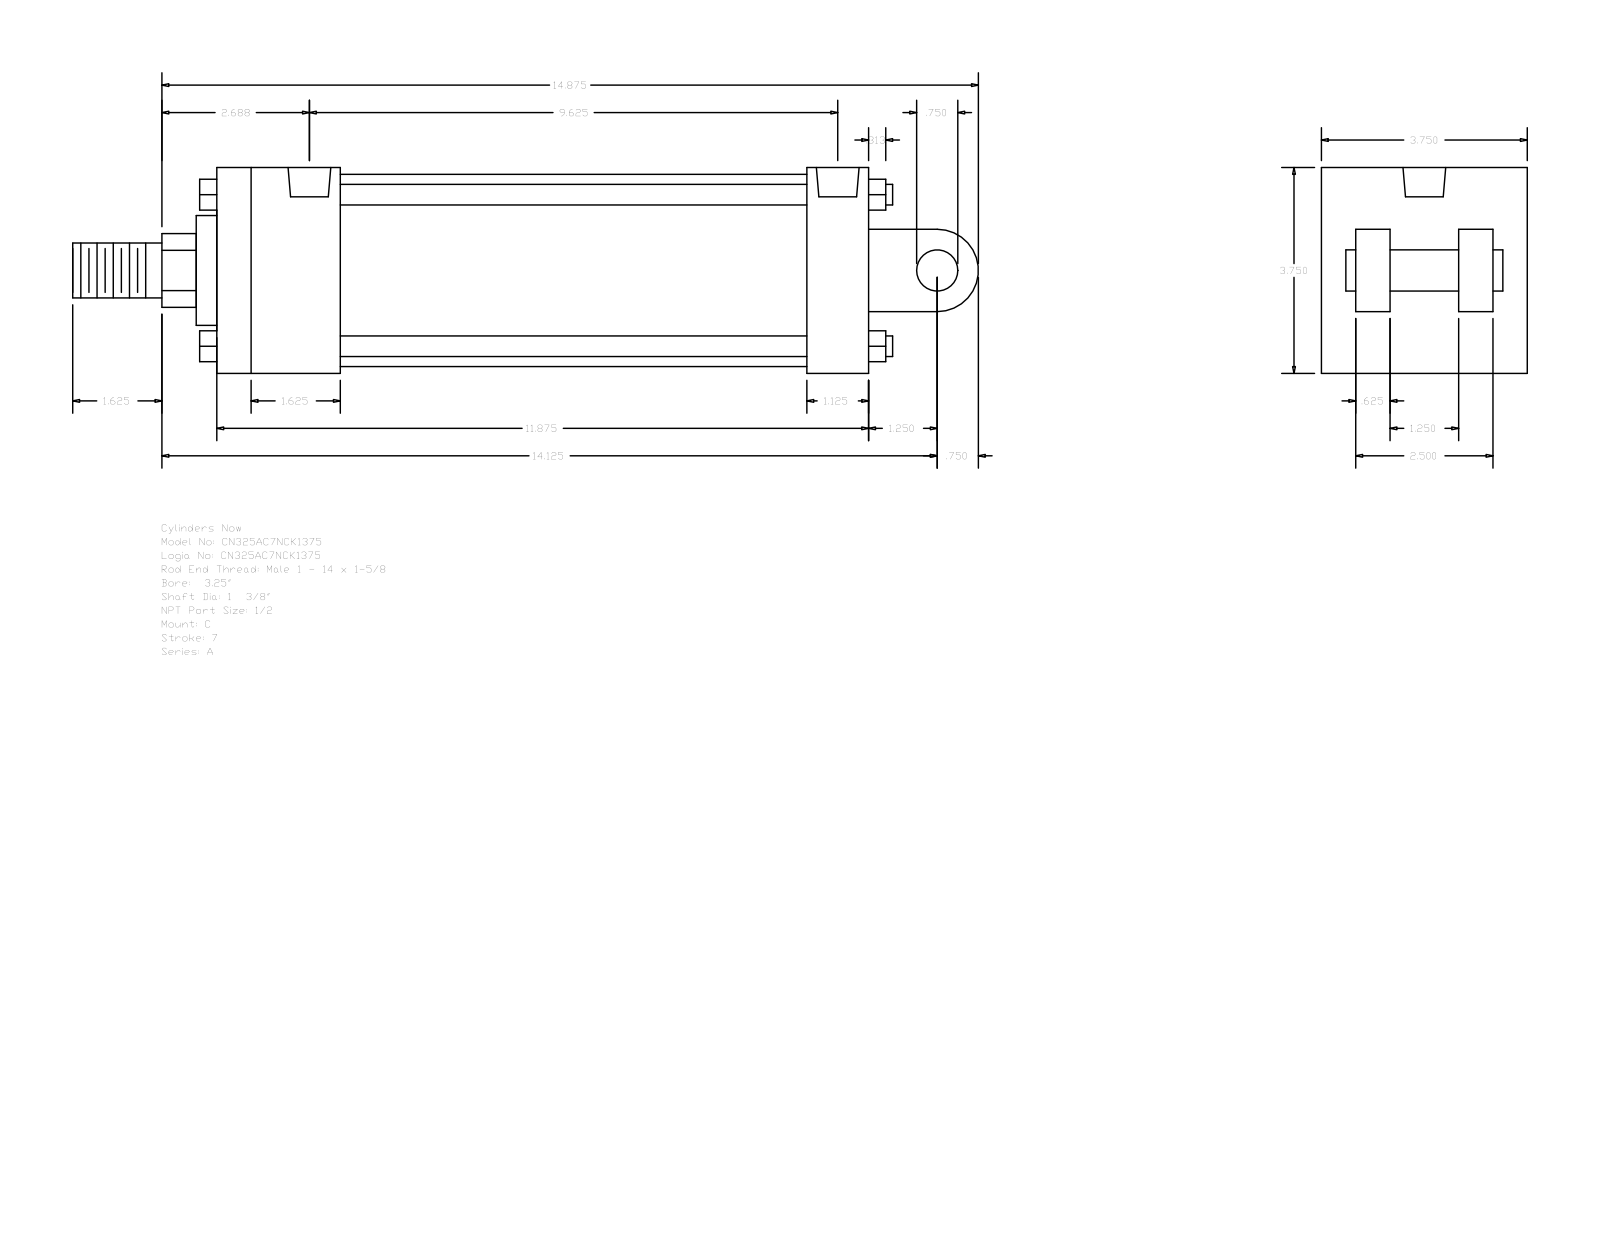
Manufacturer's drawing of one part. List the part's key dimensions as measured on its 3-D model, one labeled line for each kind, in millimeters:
Part name (STEP PRODUCT): A_C__0325_1.375
STEP written by: GSSL Pune (CONFIG_CONTROL_DESIGN)
Units: millimetres
Bodies: 0 solids, 135 faces (102 planar, 33 cylindrical, 0 other)
Overall size (bounding box): 419.1 × 95.25 × 95.25
Round holes (diameter × count): ⌀8.73 ×4, ⌀19.77 ×2
Round bosses / shafts (diameter × count): ⌀9.53 ×4, ⌀88.9 ×1, ⌀50.8 ×1, ⌀34.92 ×1, ⌀25.4 ×1, ⌀19.05 ×1
Partial cylindrical surfaces — rounded edges, fillets, slot ends (radius × count): R17.06 ×1, R19.05 ×1
Main face-to-face distances: 95.24, 301.62, 15.87, 28.57, 63.5, 66.67, 57.15, 79.37, 31.74, 47.63
Hole centre spacings: 3.18, 238.12, 241.3, 244.48
